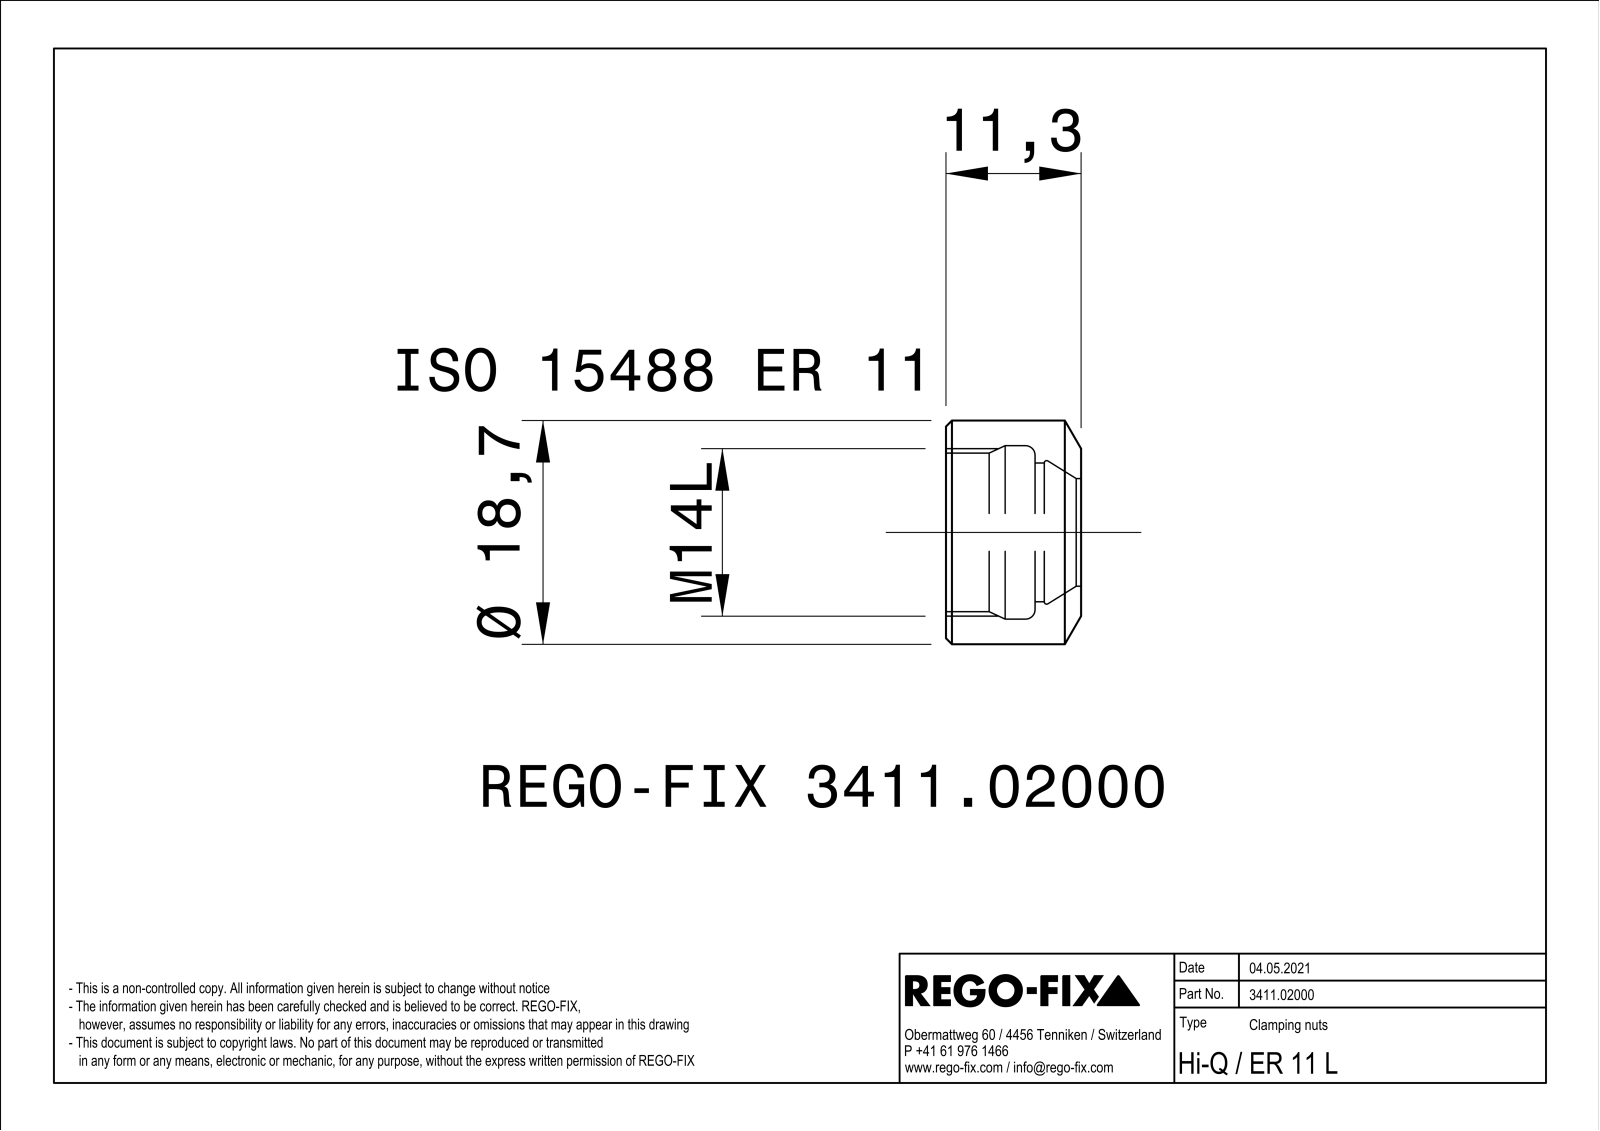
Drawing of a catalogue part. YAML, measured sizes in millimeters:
part_name: "NOCUT"
step_written_by: "SIEMENS PLM Software Solid Edge ST10 (AUTOMOTIVE_DESIGN)"
units: millimeters
bodies: {solids: 1, faces: 31, planar: 16, cylindrical: 6, other: 9}
overall_size: [18.7, 18.7, 11.3]
volume: 1423
surface_area: 1446
round_holes:
  - {diameter: 9, count: 1}
  - {diameter: 11.6, count: 1}
  - {diameter: 13.19, count: 1}
  - {diameter: 14.5, count: 1}
round_bosses_or_shafts:
  - {diameter: 18.7, count: 1}
face_to_face_distances: [17, 11.3, 3.85, 7.45, 3.1, 0.75, 8.2]
